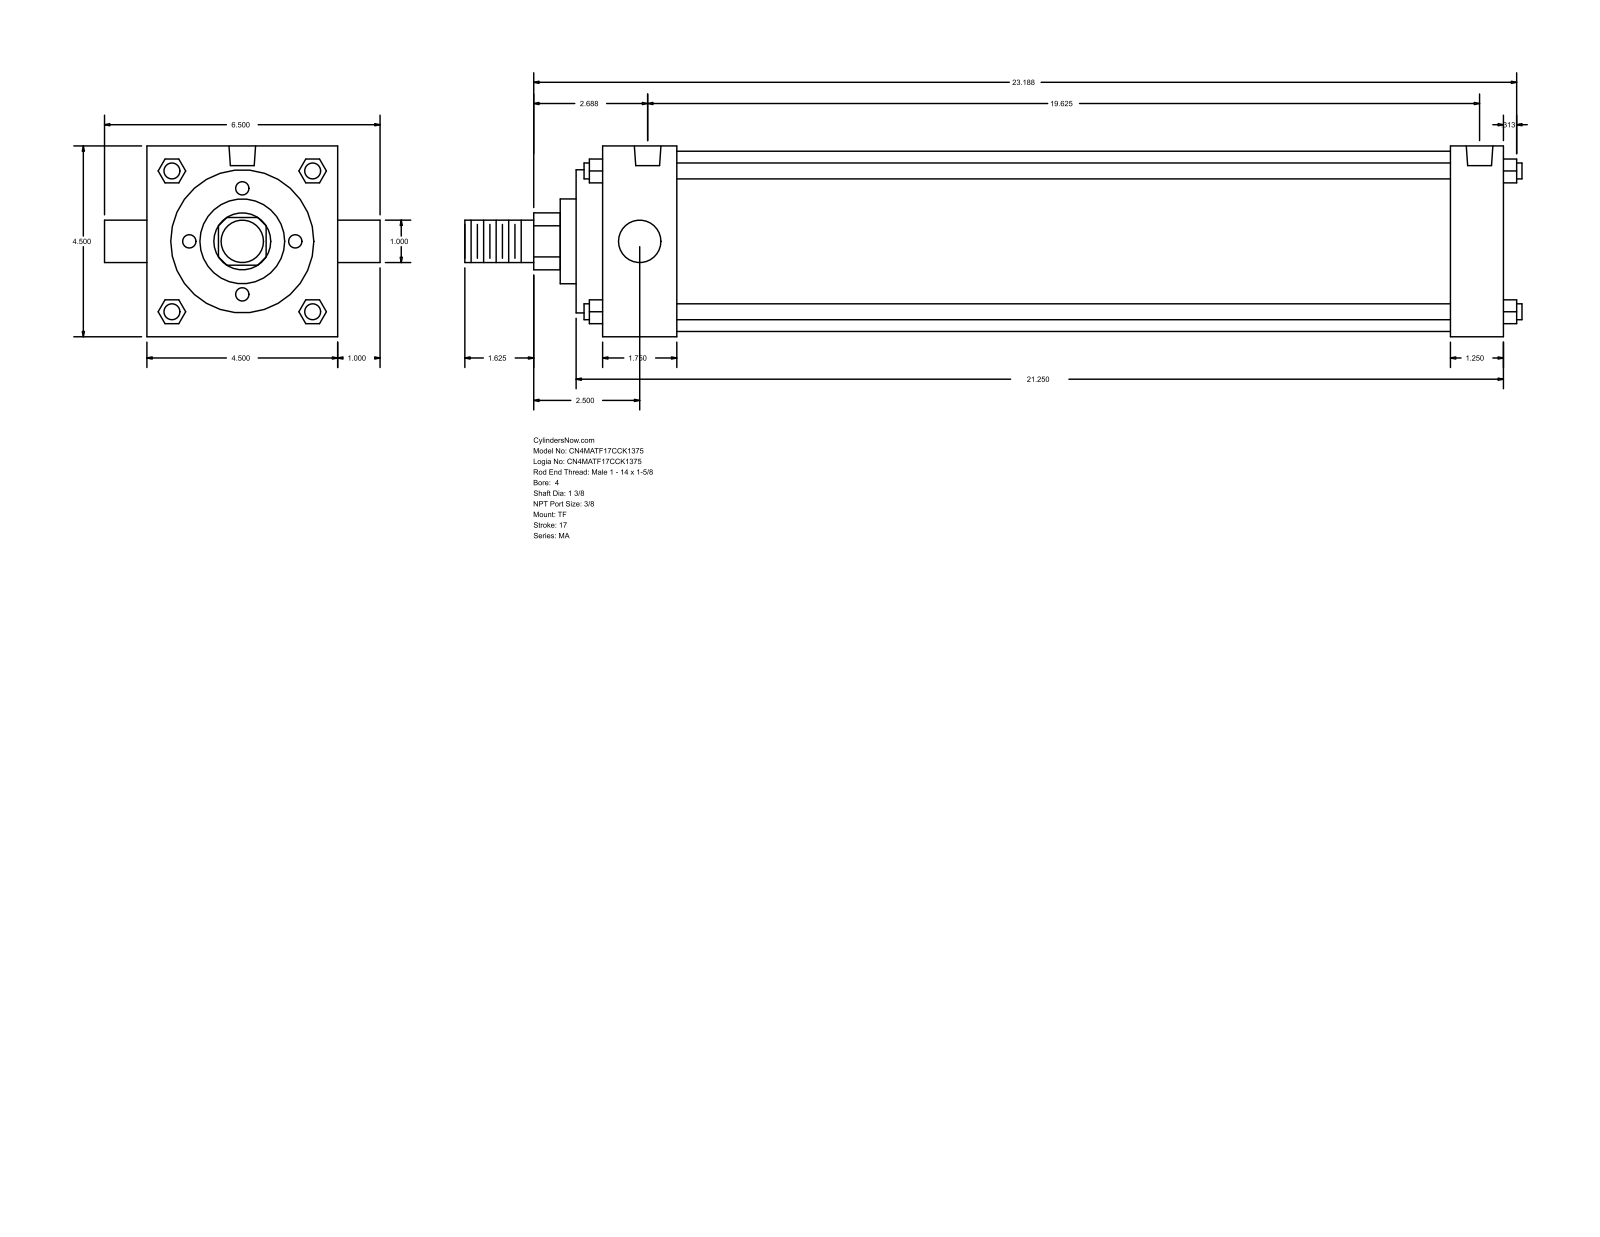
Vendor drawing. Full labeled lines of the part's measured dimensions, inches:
Part name (STEP PRODUCT): MA_TF__0400_1.375
STEP written by: GSSL Pune (CONFIG_CONTROL_DESIGN)
Units: inches
Bodies: 0 solids, 122 faces (93 planar, 29 cylindrical, 0 other)
Overall size (bounding box): 24.937 × 6.5 × 4.5
Round holes (diameter × count): ⌀0.437 ×3, ⌀0.627 ×2
Round bosses / shafts (diameter × count): ⌀0.375 ×4, ⌀1 ×2, ⌀4.25 ×1, ⌀3.375 ×1, ⌀2 ×1, ⌀1.375 ×1
Partial cylindrical surfaces — rounded edges, fillets, slot ends (radius × count): R0.672 ×1
Main face-to-face distances: 4.5, 21.25, 21.875, 0.625, 20.625, 20, 1.25, 2.375, 1.75, 18.25
Hole centre spacings: 0.187, 0.188, 19.25, 19.437, 19.438, 19.625
